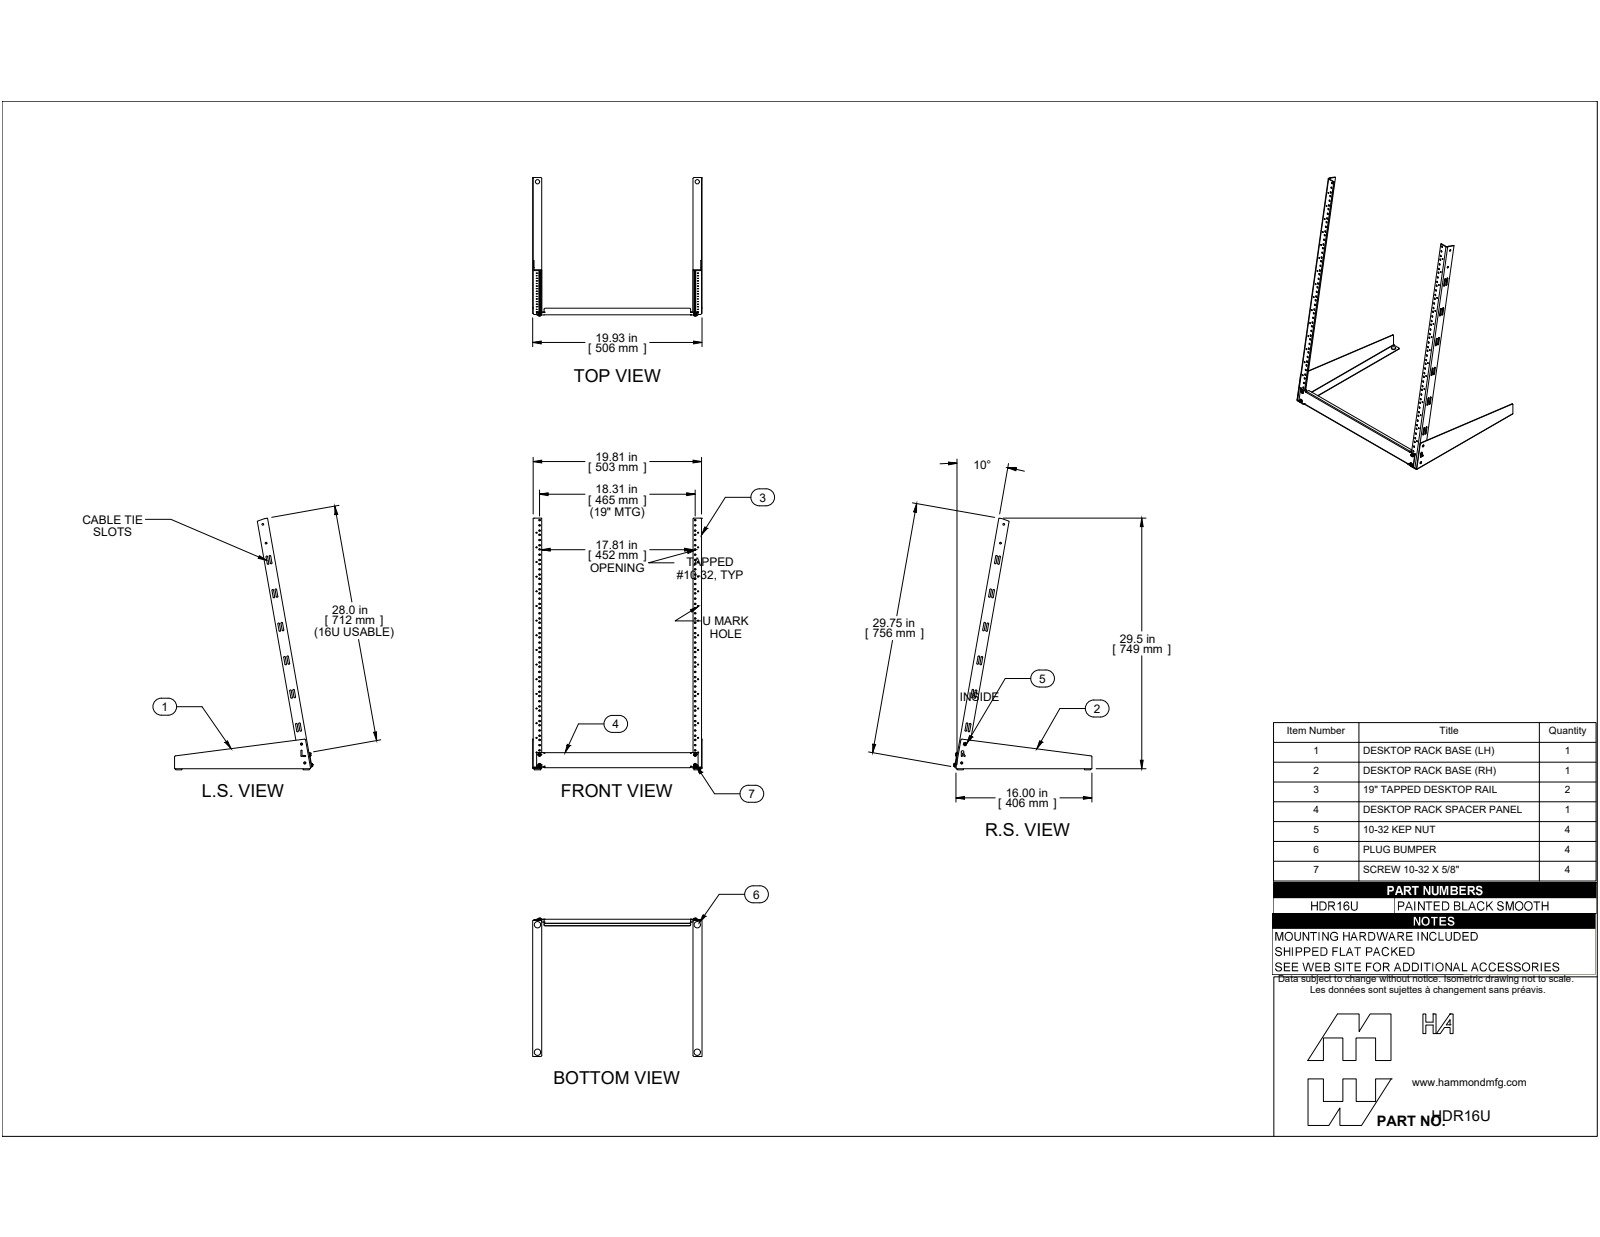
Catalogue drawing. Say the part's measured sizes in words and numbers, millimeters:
The part is named "HDR16UBK". Its 3-D file was written by "SolidWorks 2019 (CONFIG_CONTROL_DESIGN)". It is 21 solids with 528 faces: 248 planar, 272 cylindrical and 8 other. Overall it measures 752 by 506.1 by 413.3 millimeters. Its volume is 338 600 cubic millimeters and its surface area 382 200 square millimeters. Round holes: 102 of diameter 4.5, 32 of diameter 3.2, 4 of diameter 5, 4 of diameter 5.2, 4 of diameter 12.7, 2 of diameter 4, 2 of diameter 4.8. Round bosses or shafts: 8 of diameter 9.3, 4 of diameter 19.1, 4 of diameter 4.8, 2 of diameter 6.5, 2 of diameter 4.8. Partial cylindrical surfaces (rounded edges, fillets, slot ends): 24 of radius 2.4, 15 of radius 3.2, 7 of radius 1.6, 4 of radius 0.7, 4 of radius 2.2, 2 of radius 1.2, 2 of radius 3.6, 1 of radius 4. The main face-to-face distances are 1.4, 504.7, 503.3, 2.4, 3.9, 2.4, 506.1, 502.3, 500.8, 3.9. The hole center spacings are 28.6, 177.8, 266.7, 444.5, 60.3, 88.9, 149.2, 57.2.
